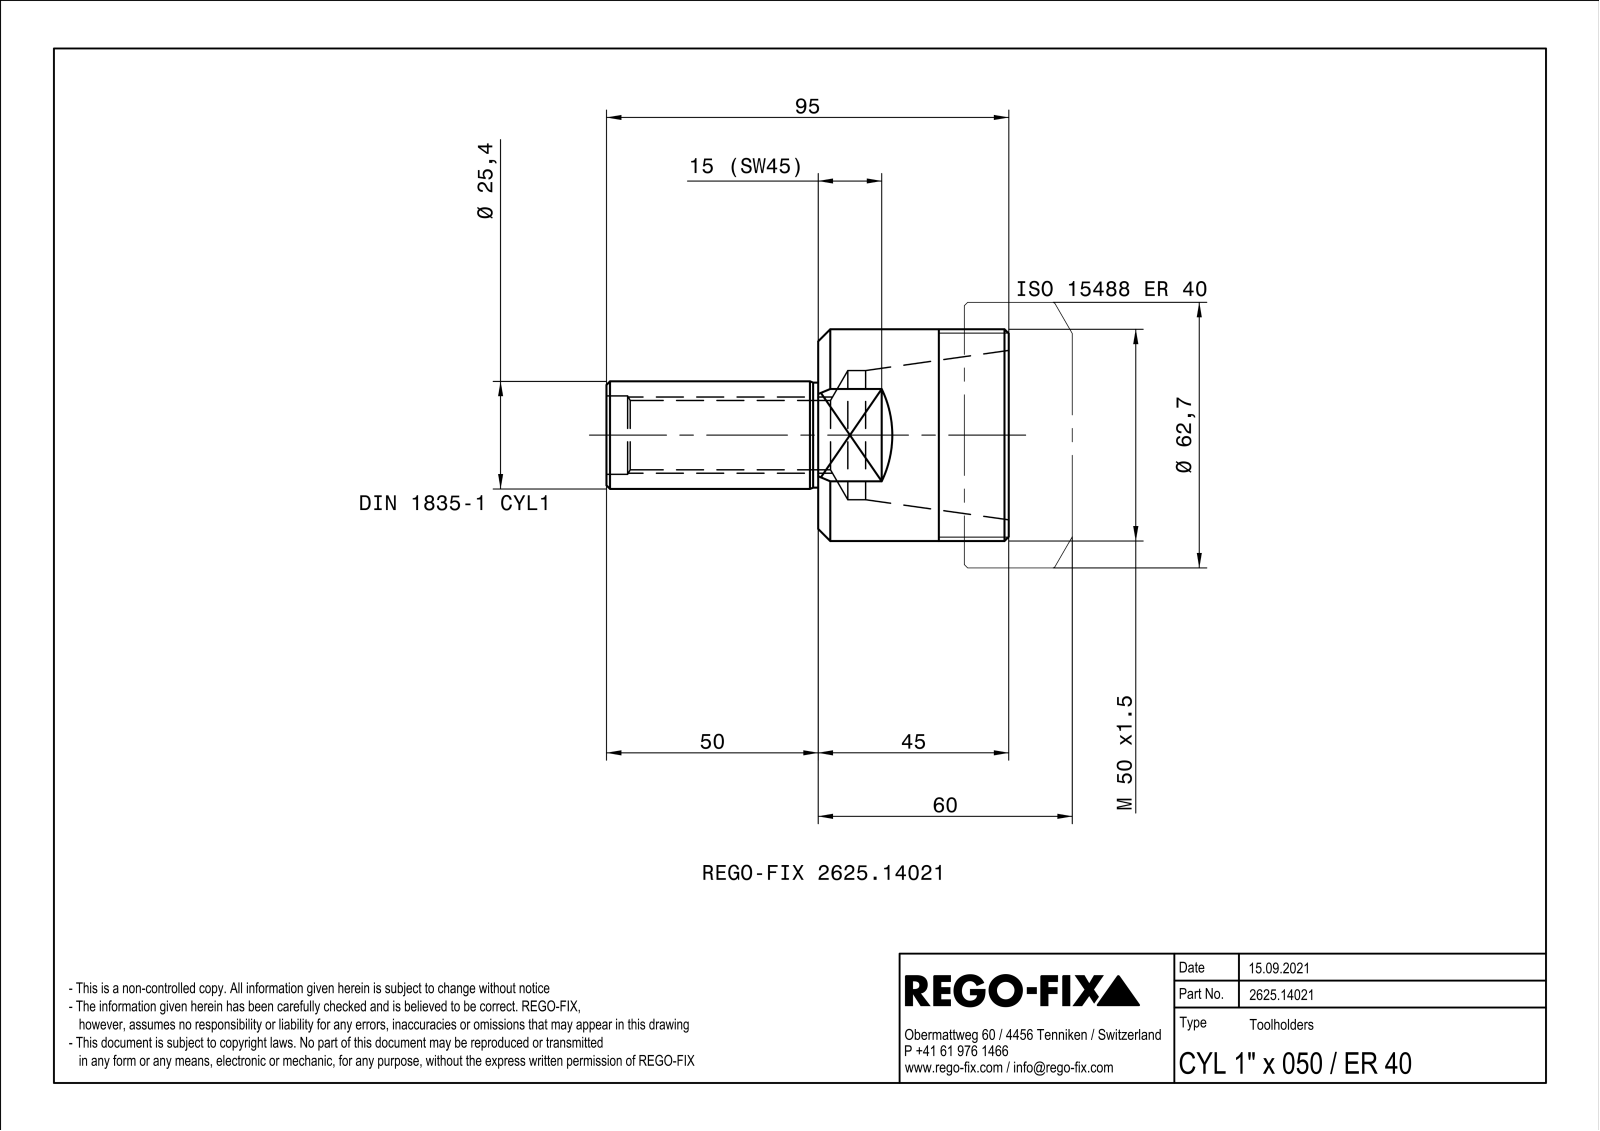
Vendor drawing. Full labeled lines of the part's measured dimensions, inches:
Part name (STEP PRODUCT): NOCUT
STEP written by: SIEMENS PLM Software Solid Edge ST10 (AUTOMOTIVE_DESIGN)
Units: inches
Bodies: 1 solid, 27 faces (9 planar, 7 cylindrical, 11 other)
Overall size (bounding box): 3.74 × 1.969 × 1.969
Volume: 3.805 in³ · Surface area: 31.84 in²
Round holes (diameter × count): ⌀0.645 ×1, ⌀0.728 ×1, ⌀1.201 ×1
Round bosses / shafts (diameter × count): ⌀1.969 ×1, ⌀1 ×1, ⌀0.984 ×1
Main face-to-face distances: 1.772, 3.74, 1.969, 0.376
